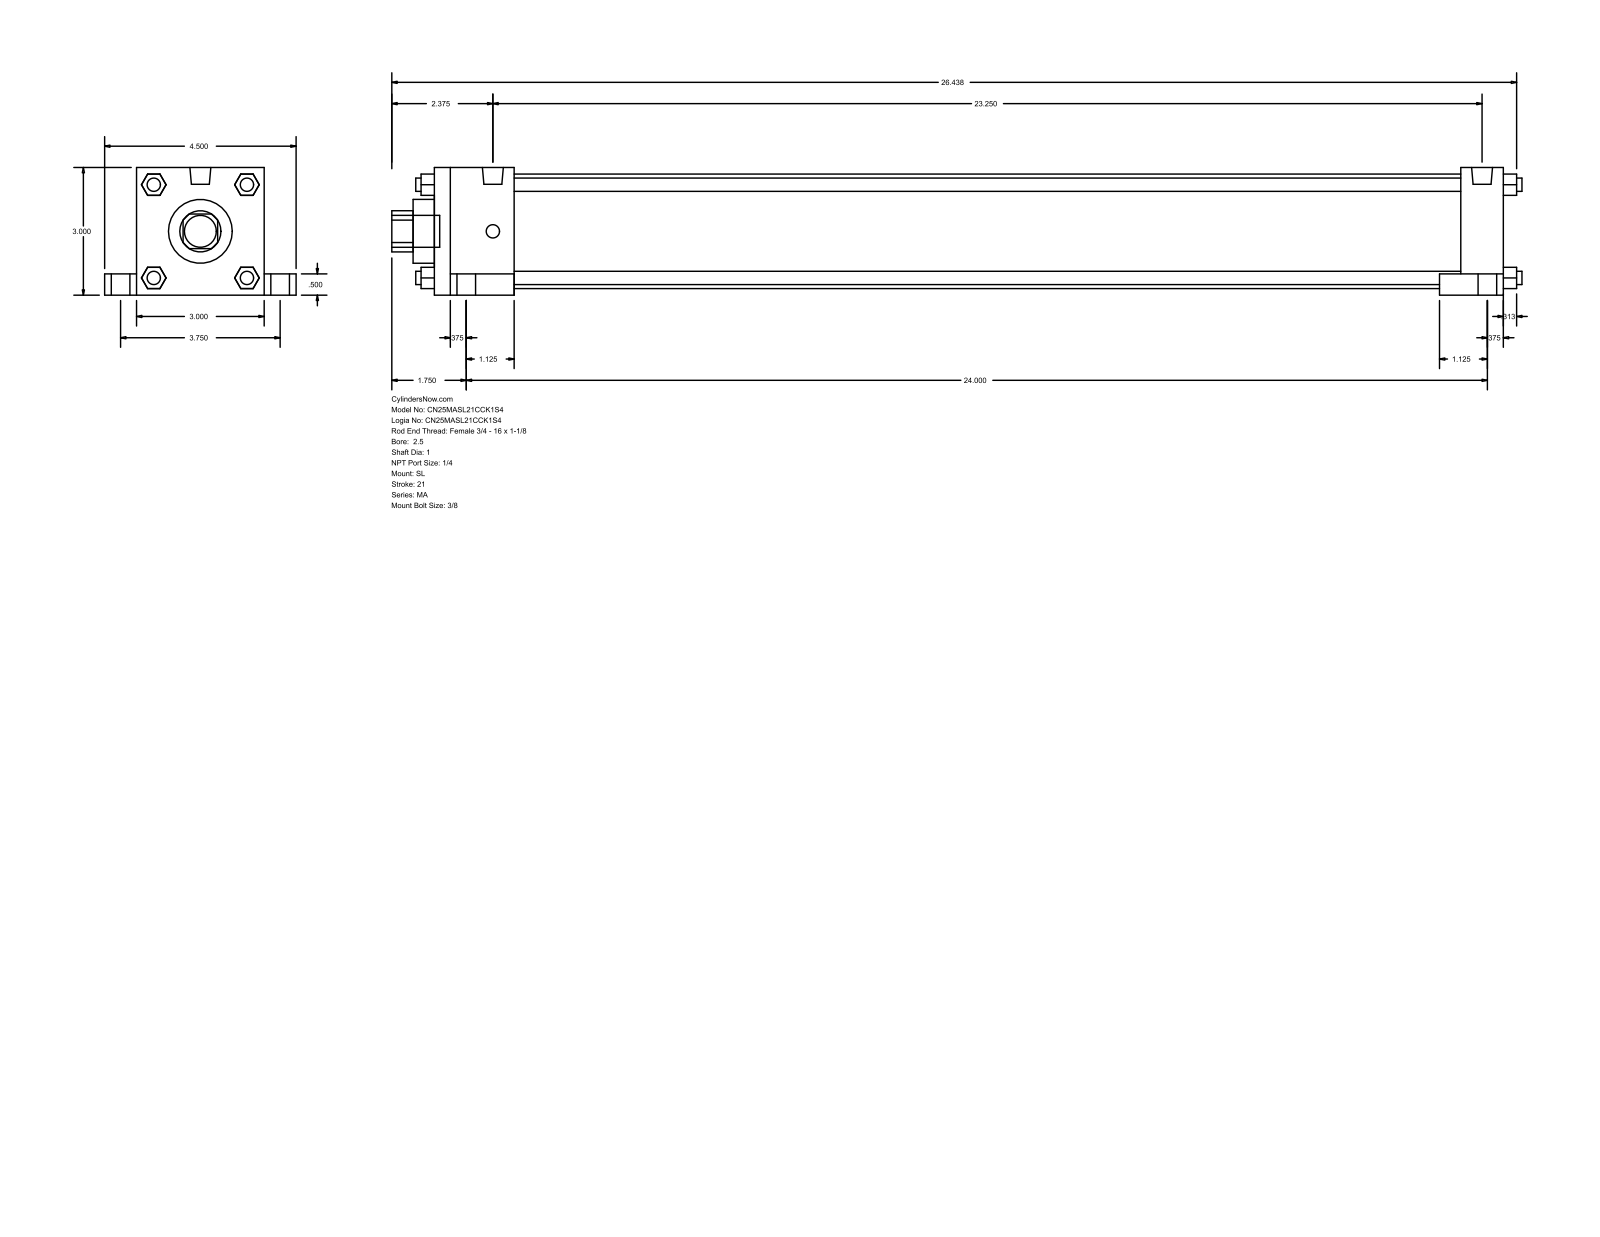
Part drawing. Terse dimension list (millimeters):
name: MA_SL__0250_1
written by: GSSL Pune (CONFIG_CONTROL_DESIGN)
unit: mm
bodies: 0 solids, 148 faces (112 planar, 36 cylindrical, 0 other)
size: 674.69 × 114.3 × 76.2
holes: 1× ⌀25.4, 1× ⌀38.1, 1× ⌀68.33
bosses: 8× ⌀7.94, 4× ⌀17.46, 4× ⌀11.11, 2× ⌀12.49, 1× ⌀19.05
rounds: 1× R12.29
face distances: 76.2, 638.18, 12.7, 47.63, 590.55, 612.77, 565.14, 25.41, 19.05, 95.25
